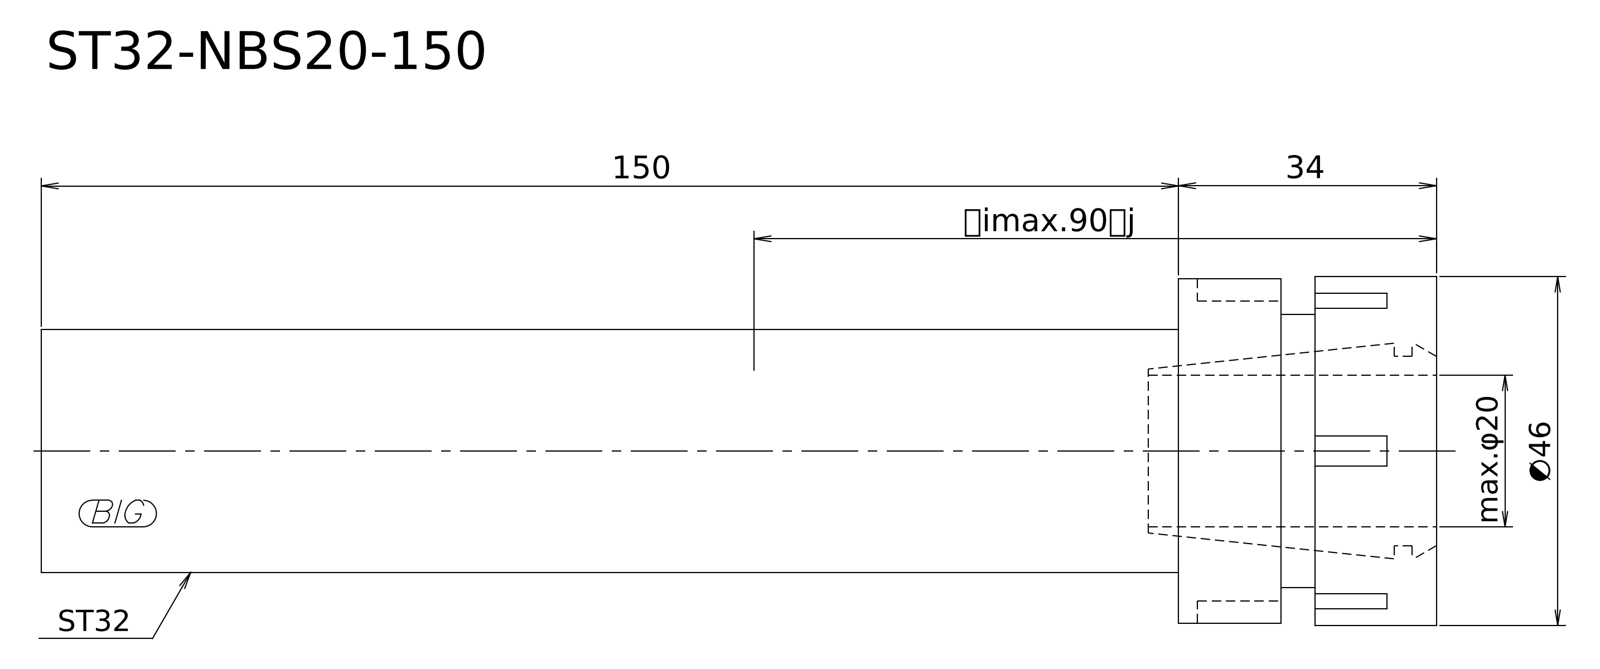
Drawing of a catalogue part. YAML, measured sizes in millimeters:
step_written_by: "Kubotek KeyCreator V8.5.1 (14335) (CONFIG_CONTROL_DESIGN)"
units: millimeters
bodies: {solids: 1, faces: 9, planar: 5, cylindrical: 4, other: 0}
overall_size: [184, 46, 46]
volume: 173759
surface_area: 24371
round_bosses_or_shafts:
  - {diameter: 46, count: 1}
  - {diameter: 45.5, count: 1}
  - {diameter: 36, count: 1}
  - {diameter: 32, count: 1}
face_to_face_distances: [34, 184, 150, 16, 18, 168, 20.5, 4.5, 13.5, 163.5]
